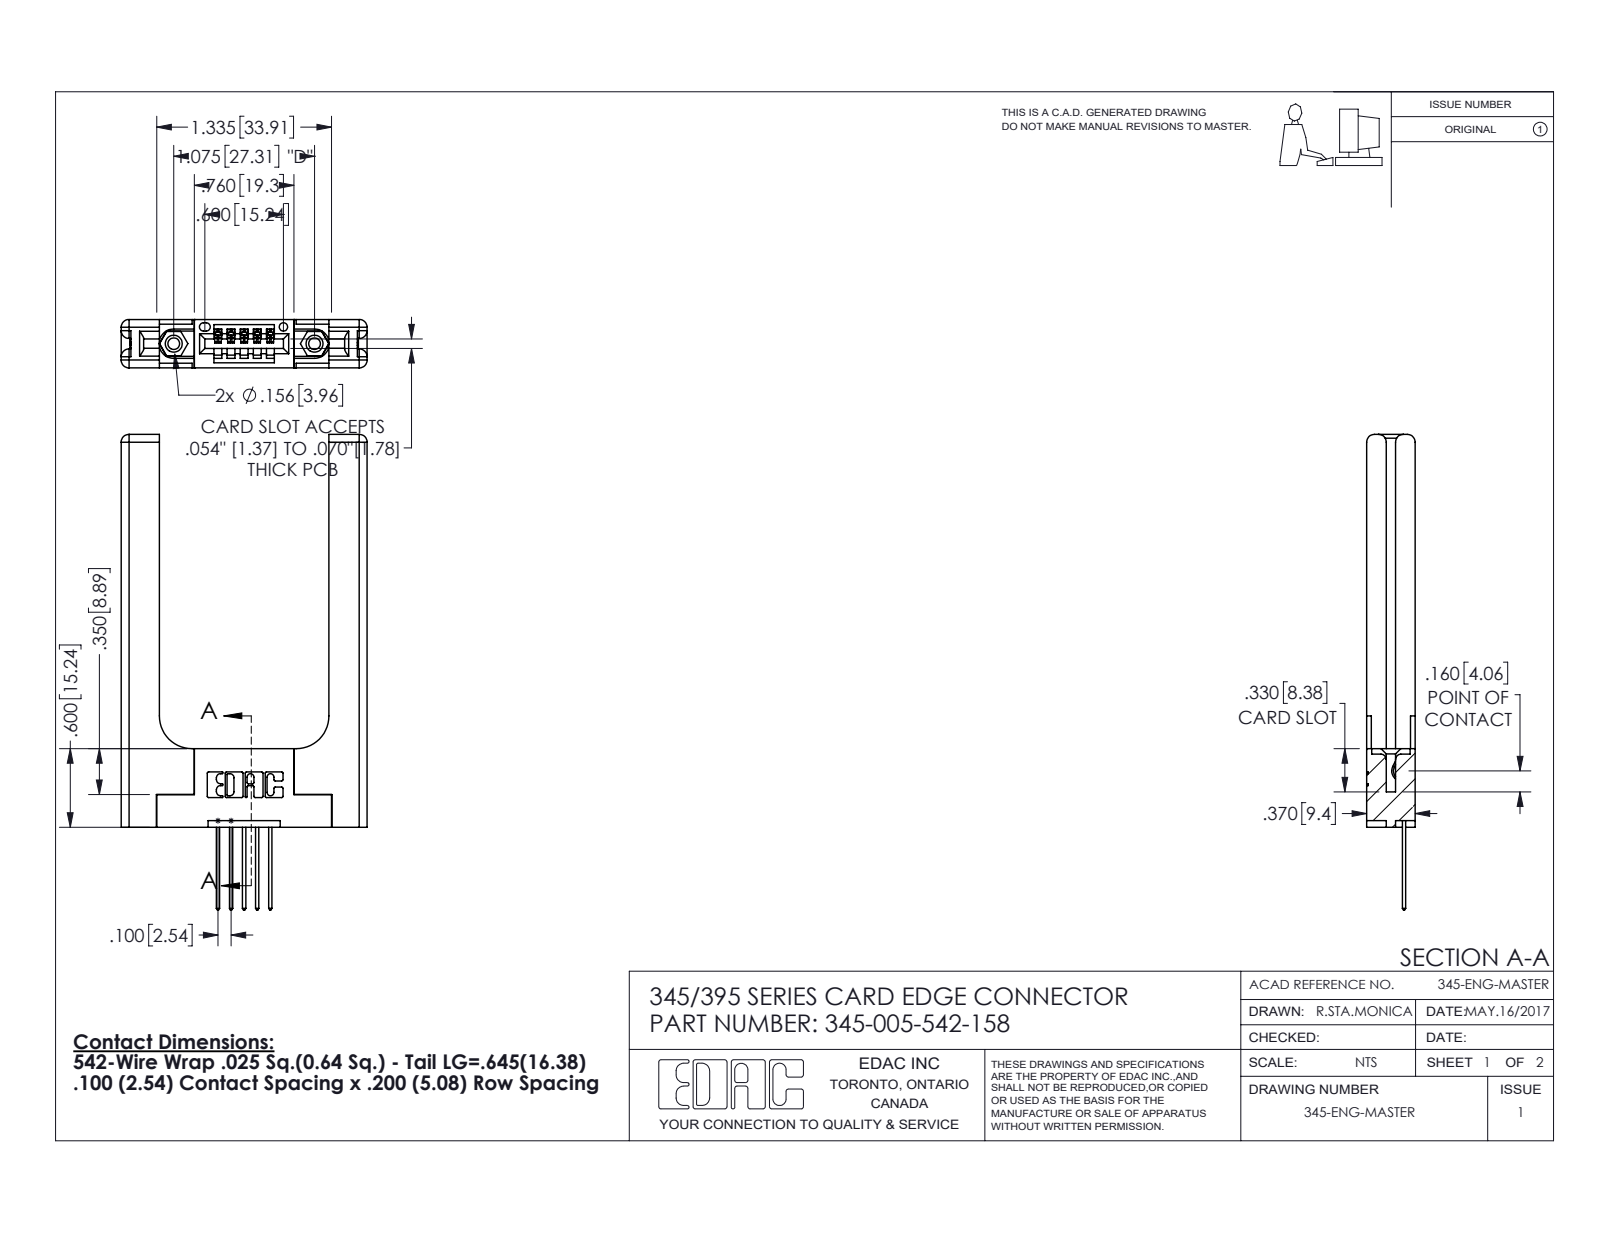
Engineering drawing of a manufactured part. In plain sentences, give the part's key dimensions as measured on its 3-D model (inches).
The part is named "345-220-058_345-220-058; 345 Part_Flush Mounting Lugs - 0.156 Dia-TH; 345-250-001_345-250-001-102; 345-292-001_345-293-142 (+1 more)". Its 3-D file was written by "SolidWorks 2016 (CONFIG_CONTROL_DESIGN)". It is 10 solids with 672 faces: 428 planar, 184 cylindrical and 60 other. Overall it measures 3.632 by 1.879 by 0.37 inches. Its volume is 0.778 cubic inches and its surface area 16.29 square inches. Round holes: 2 of diameter 0.089, 2 of diameter 0.125, 2 of diameter 0.156, 1 of diameter 0.064. Round bosses or shafts: 2 of diameter 0.155. Partial cylindrical surfaces (rounded edges, fillets, slot ends): 22 of radius 0.01, 16 of radius 0.06, 10 of radius 0.006, 10 of radius 0.01, 6 of radius 0.007, 6 of radius 0.031, 3 of radius 0.026, 2 of radius 0.03. The main face-to-face distances are 0.37, 0.15, 0.22, 0.072, 1.296, 0.077, 0.148, 0.298, 0.071, 0.2. The hole center spacings are 0.27, 0.847, 1.075.
